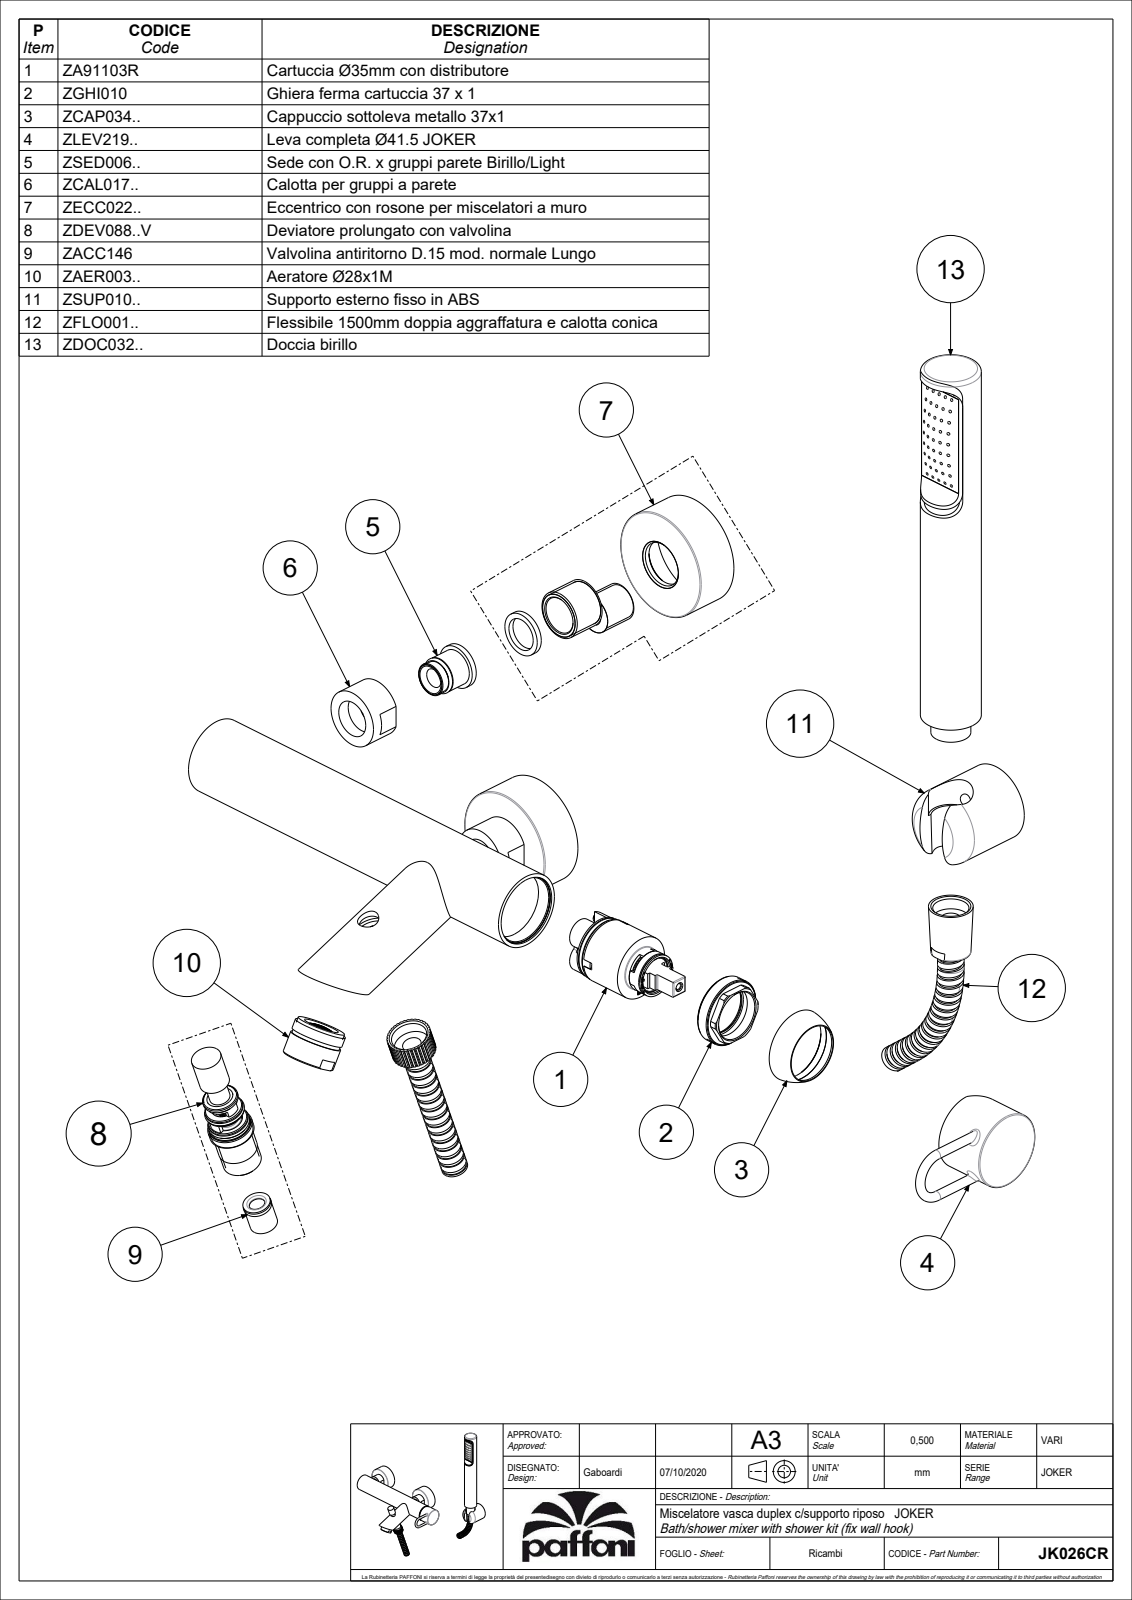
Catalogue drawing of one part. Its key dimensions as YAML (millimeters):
part_name: "JK026CR"
step_written_by: "CREO PARAMETRIC BY PTC INC, 2020044 (CONFIG_CONTROL_DESIGN)"
units: millimeters
bodies: {solids: 5, faces: 3354, planar: 2325, cylindrical: 669, other: 360}
overall_size: [466.15, 400.85, 171.48]
volume: 514657
surface_area: 224776
round_holes:
  - {diameter: 1.5, count: 45}
  - {diameter: 5, count: 7}
  - {diameter: 7.5, count: 6}
  - {diameter: 8, count: 5}
  - {diameter: 12, count: 5}
  - {diameter: 9, count: 3}
  - {diameter: 16, count: 3}
  - {diameter: 18, count: 3}
  - {diameter: 24.5, count: 3}
  - {diameter: 4, count: 2}
  - {diameter: 10.5, count: 2}
  - {diameter: 16.7, count: 2}
round_bosses_or_shafts:
  - {diameter: 13, count: 6}
  - {diameter: 5, count: 5}
  - {diameter: 24, count: 3}
  - {diameter: 59.7, count: 2}
  - {diameter: 35, count: 2}
  - {diameter: 31.5, count: 2}
  - {diameter: 21, count: 2}
  - {diameter: 20.6, count: 2}
partial_cylinders:
  - {radius: 0.5, count: 44}
  - {radius: 0.15, count: 11}
  - {radius: 0.3, count: 9}
  - {radius: 1, count: 4}
  - {radius: 7, count: 4}
  - {radius: 1.56, count: 2}
  - {radius: 4.5, count: 2}
  - {radius: 7.8, count: 2}
face_to_face_distances: [5, 3.5, 19.5, 10, 25, 14.5, 2.5, 39.5, 1, 3]
hole_center_spacings: [7.91, 13.76, 6.5, 13, 20.01, 26.39, 4.5, 19.5]
